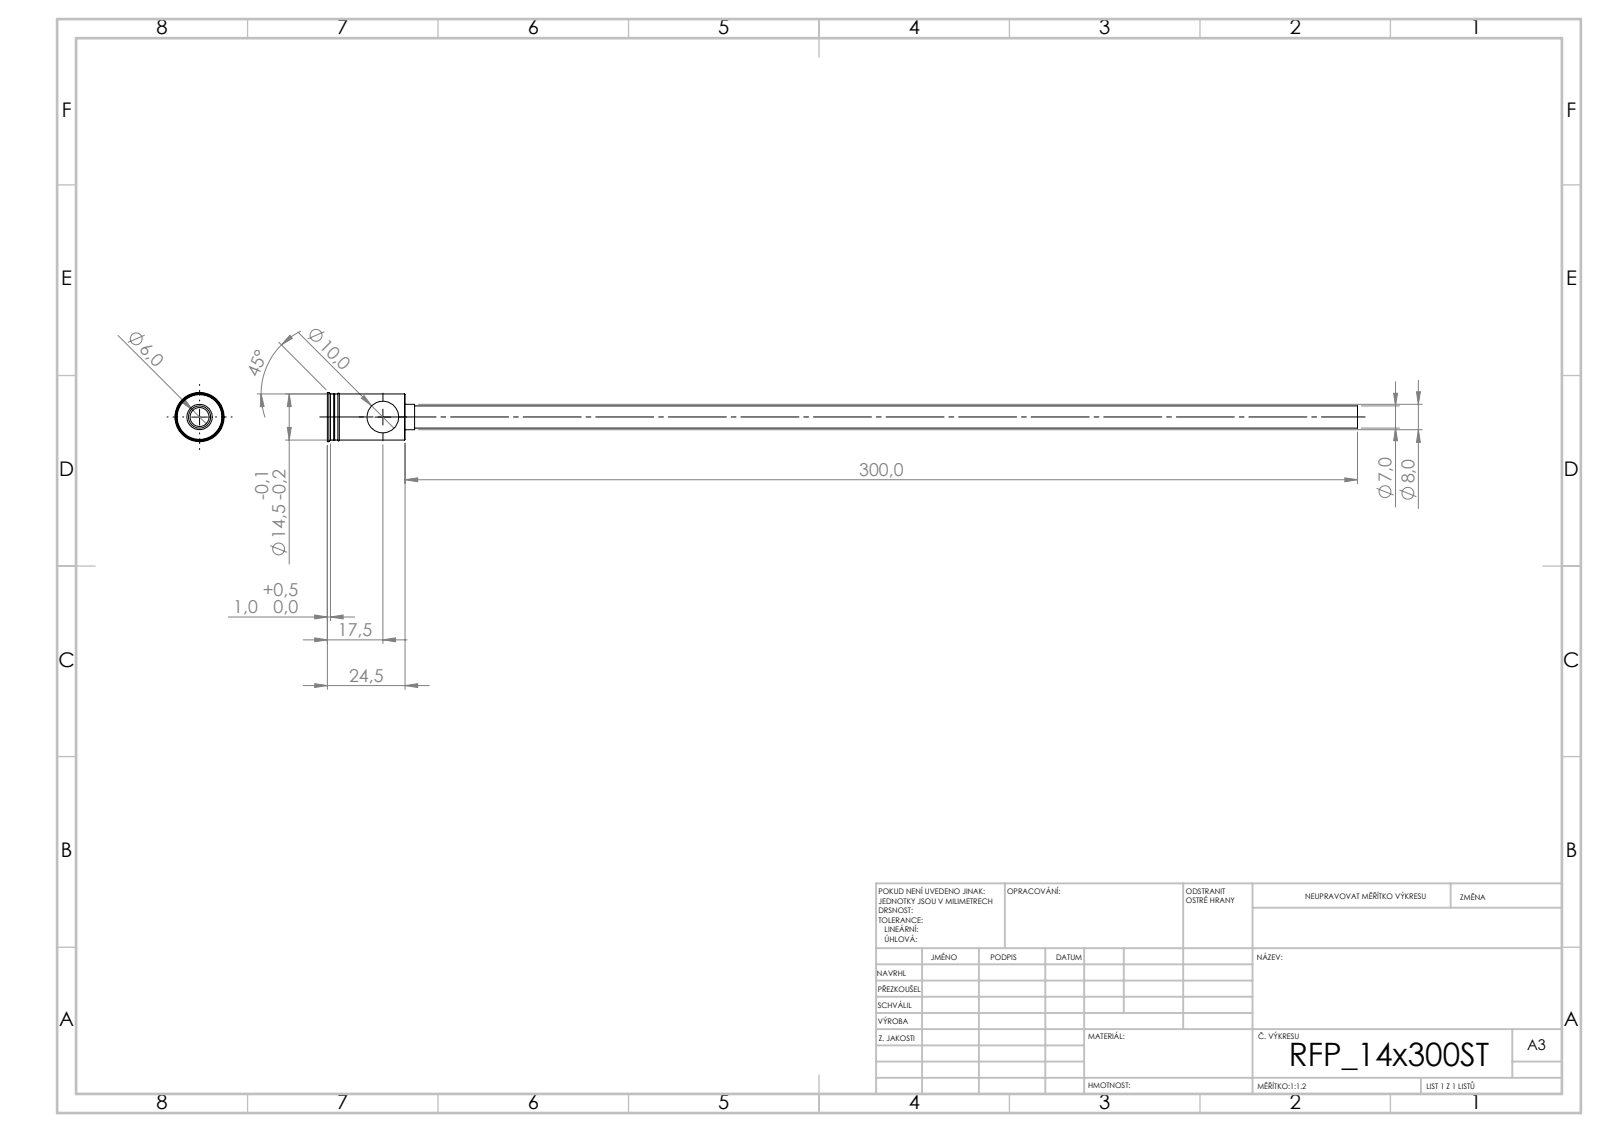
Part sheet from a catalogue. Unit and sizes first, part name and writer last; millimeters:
Units: millimetres
Overall size (bounding box): 324.5 × 15.5 × 15.5
Round holes (diameter × count): ⌀6 ×1, ⌀10 ×1
Round bosses / shafts (diameter × count): ⌀15.5 ×1, ⌀14.5 ×1, ⌀8 ×1, ⌀7 ×1
Main face-to-face distances: 24.5, 22.5, 2, 9.9, 22.2, 2.3, 3, 25.2, 25.5, 27.5
Volume: 5 864 mm³ · Surface area: 14 055 mm²
Bodies: 1 solid, 44 faces (20 planar, 16 cylindrical, 8 other)
STEP written by: SolidWorks 2019 (CONFIG_CONTROL_DESIGN)
